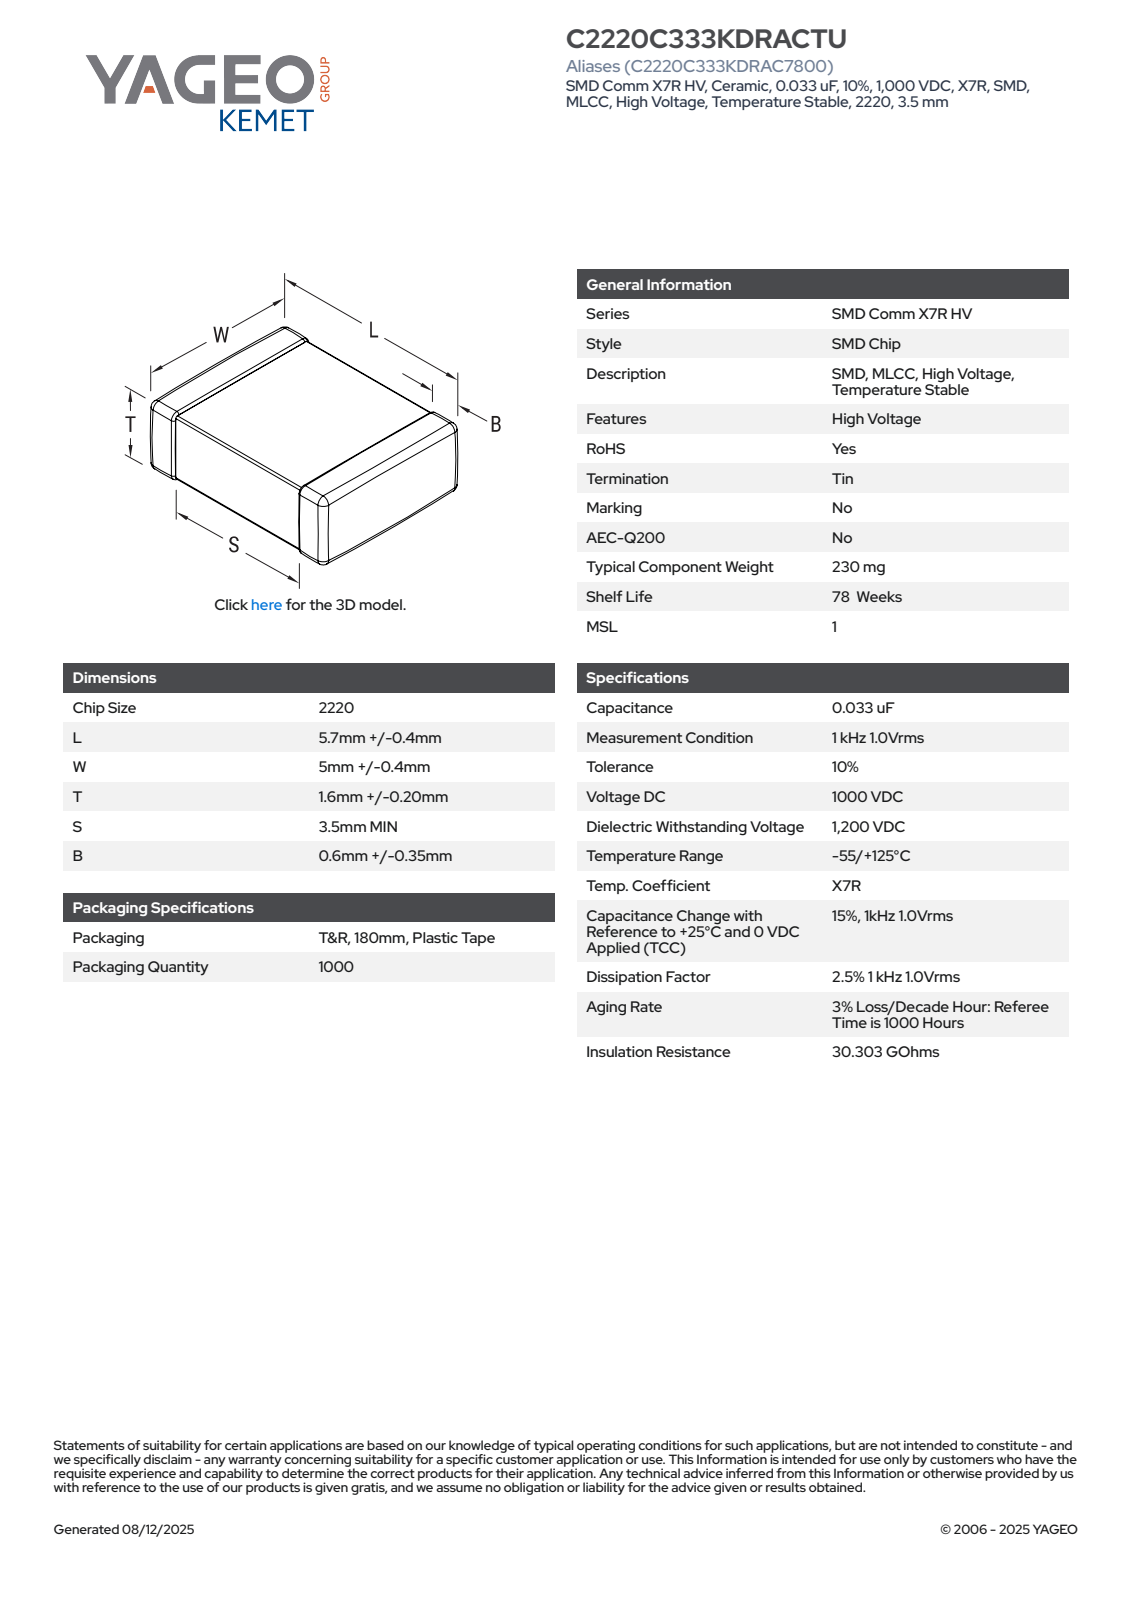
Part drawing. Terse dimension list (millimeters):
name: CCS_CCSTD_2220_L6.1W5.4T1.8B0.6
written by: SolidWorks 2021 (AUTOMOTIVE_DESIGN)
unit: mm
bodies: 4 solids, 125 faces (71 planar, 38 cylindrical, 16 other)
size: 6.1 × 5.4 × 1.8
volume: 53 mm³; area: 107 mm²
rounds: 24× R0.11
face distances: 1.58, 1.69, 6.1, 1.8, 5.18, 5.29, 5.4, 2.5, 3.6, 3.29
